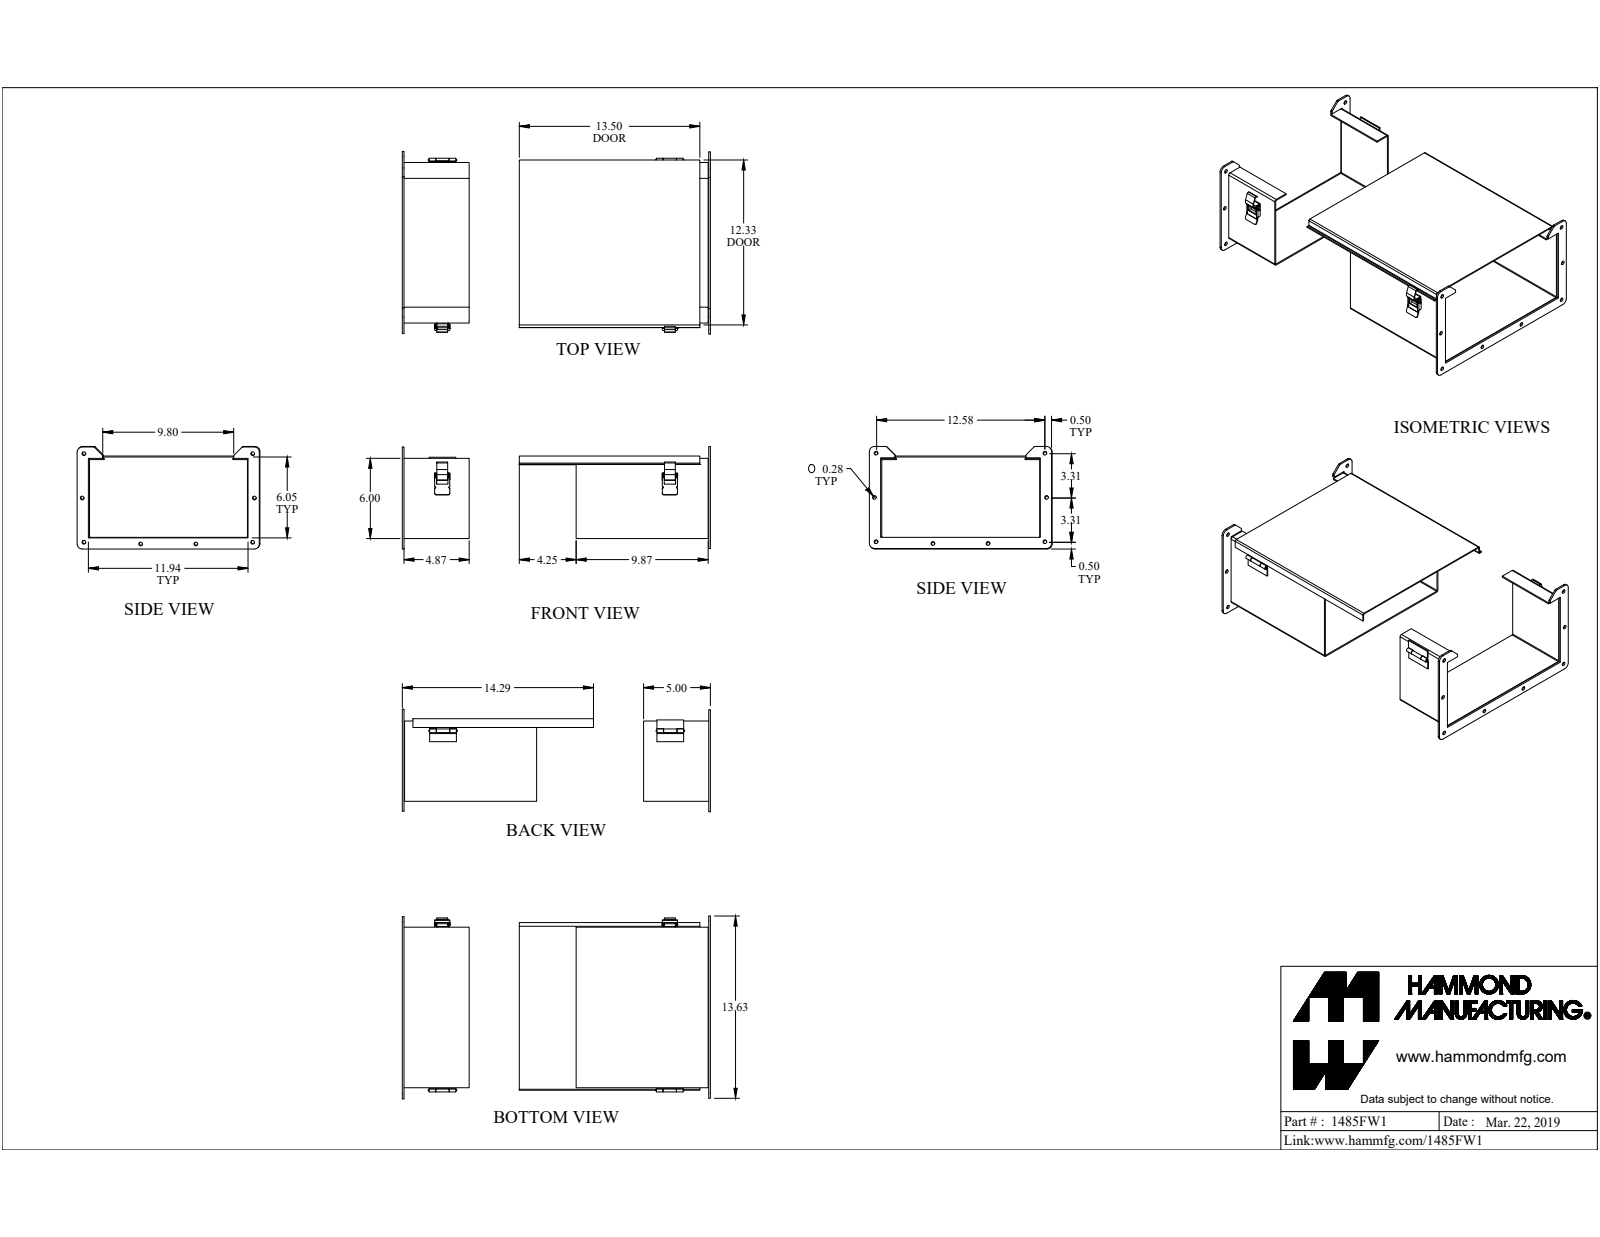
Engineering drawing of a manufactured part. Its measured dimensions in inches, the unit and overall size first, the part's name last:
Units: inches
Overall size (bounding box): 15.038 × 13.67 × 7.667
Round holes (diameter × count): ⌀0.281 ×16, ⌀0.13 ×2, ⌀0.125 ×1, ⌀0.164 ×1
Round bosses / shafts (diameter × count): ⌀0.187 ×3, ⌀0.125 ×2, ⌀0.275 ×1, ⌀0.156 ×1, ⌀0.125 ×1
Partial cylindrical surfaces — rounded edges, fillets, slot ends (radius × count): R0.016 ×13, R0.125 ×13, R0.375 ×8, R0.035 ×6, R0.039 ×5, R0.076 ×5, R0.015 ×4, R0.029 ×4
Main face-to-face distances: 0.095, 0.072, 11.905, 6.1, 6.172, 6.005, 6.077, 12, 11.81, 5.905
Hole centre spacings: 0.061, 13.173, 3.315, 4.252, 5.564, 7.976, 8.376, 9.169
Volume: 62.04 in³ · Surface area: 1 372 in²
Bodies: 21 solids, 440 faces (264 planar, 172 cylindrical, 4 other)
Part name (STEP PRODUCT): 1485FW1
STEP written by: SolidWorks 2019 (CONFIG_CONTROL_DESIGN)
